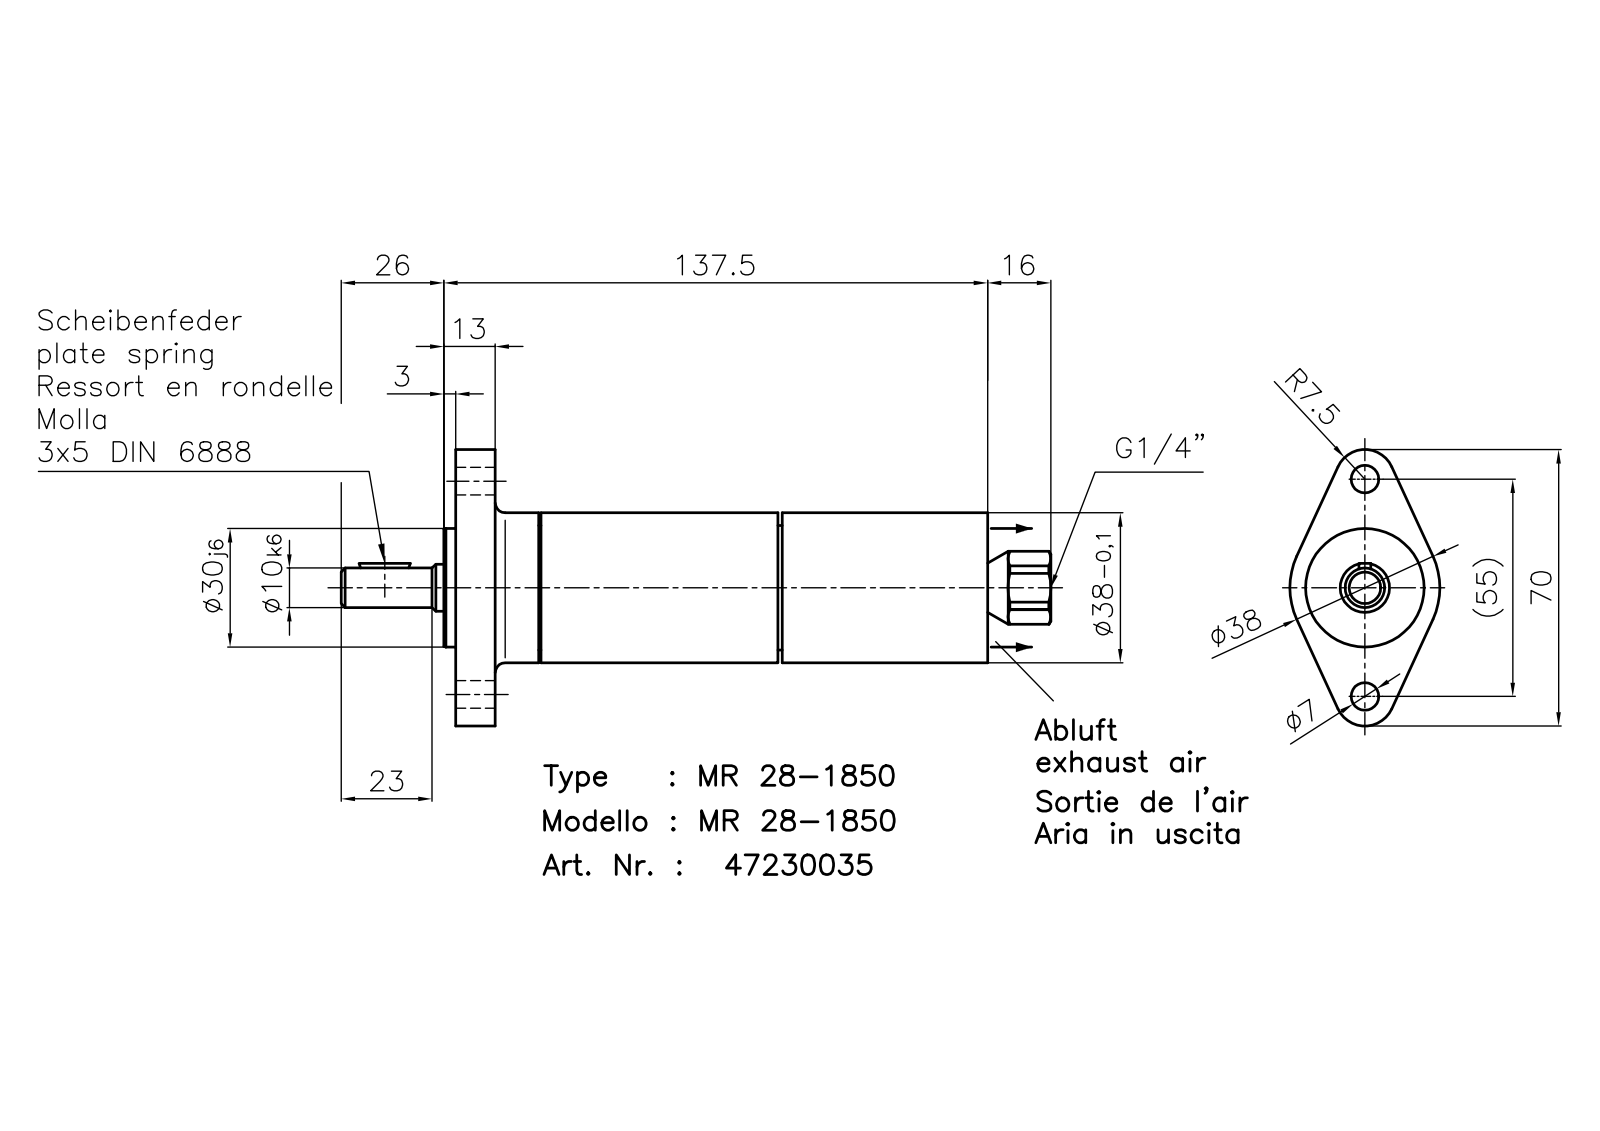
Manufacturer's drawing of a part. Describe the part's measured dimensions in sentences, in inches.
The part is named "MR 28-1850_47230035". Its 3-D file was written by "Autodesk Inventor 2008 (AUTOMOTIVE_DESIGN)". It is 1 solid with 83 faces: 37 planar, 32 cylindrical and 14 other. Overall it measures 7.071 by 2.756 by 1.496 inches. Its volume is 9.941 cubic inches and its surface area 41.63 square inches. Round holes: 2 of diameter 0.276, 1 of diameter 0.11, 1 of diameter 0.256, 1 of diameter 0.45, 1 of diameter 0.492, 1 of diameter 0.496, 1 of diameter 1.417, 1 of diameter 1.421, 1 of diameter 1.425. Round bosses or shafts: 1 of diameter 1.496, 1 of diameter 1.339, 1 of diameter 1.26, 1 of diameter 1.181, 1 of diameter 0.467, 1 of diameter 0.394. Partial cylindrical surfaces (rounded edges, fillets, slot ends): 2 of radius 0.295, 1 of radius 0.256, 1 of radius 0.266, 1 of radius 0.364, 1 of radius 0.698. The main face-to-face distances are 0.118, 5.303, 5.421, 1.495, 3.343, 0.862, 0.512, 0.394, 4.909, 0.98. The hole center spacings are 1.083, 2.165.
